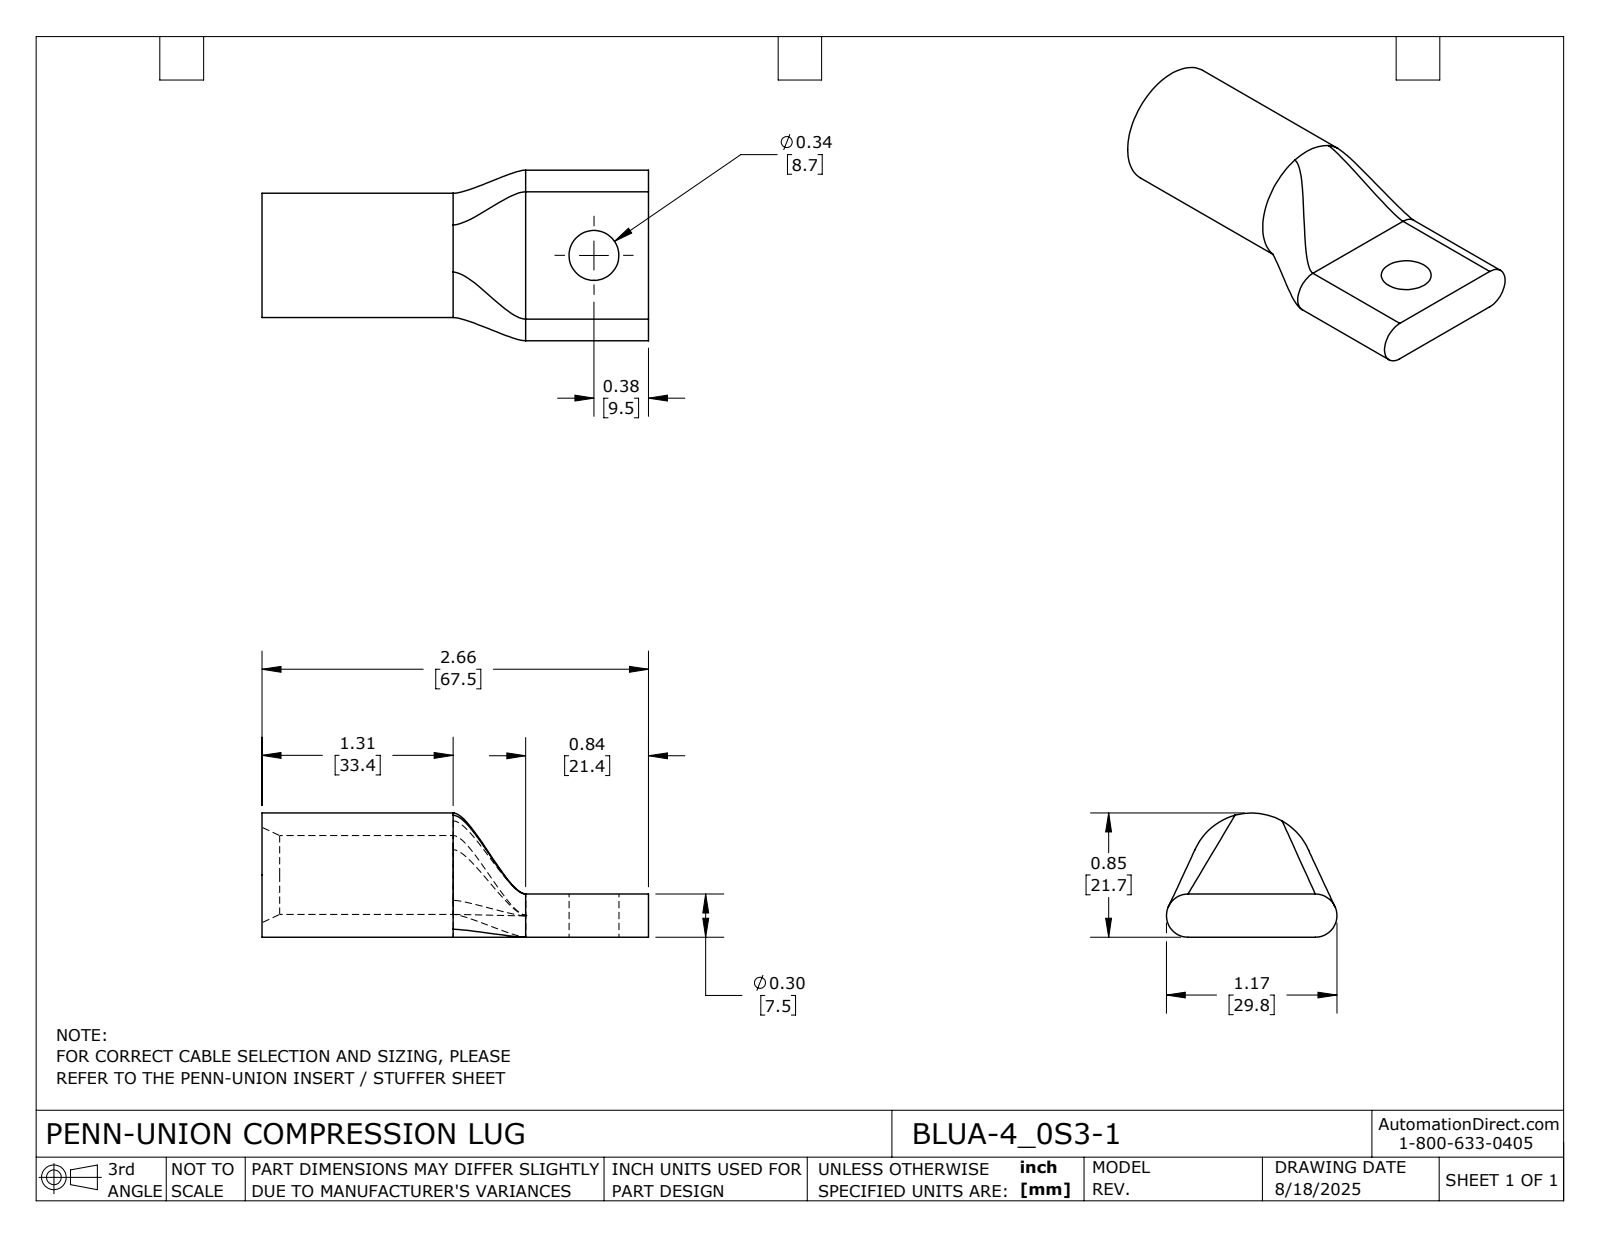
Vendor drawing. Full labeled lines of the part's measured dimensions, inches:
Part name (STEP PRODUCT): BLUA-4_0S3-1
STEP written by: SolidWorks 2024 (CONFIG_CONTROL_DESIGN)
Units: inches
Bodies: 1 solid, 24 faces (5 planar, 9 cylindrical, 10 other)
Overall size (bounding box): 2.656 × 1.172 × 0.854
Volume: 0.859 in³ · Surface area: 11.32 in²
Round holes (diameter × count): ⌀0.343 ×1, ⌀0.542 ×1
Round bosses / shafts (diameter × count): ⌀0.854 ×1
Partial cylindrical surfaces — rounded edges, fillets, slot ends (radius × count): R0.148 ×2
Main face-to-face distances: 0.297, 2.656, 1.813, 0.844
